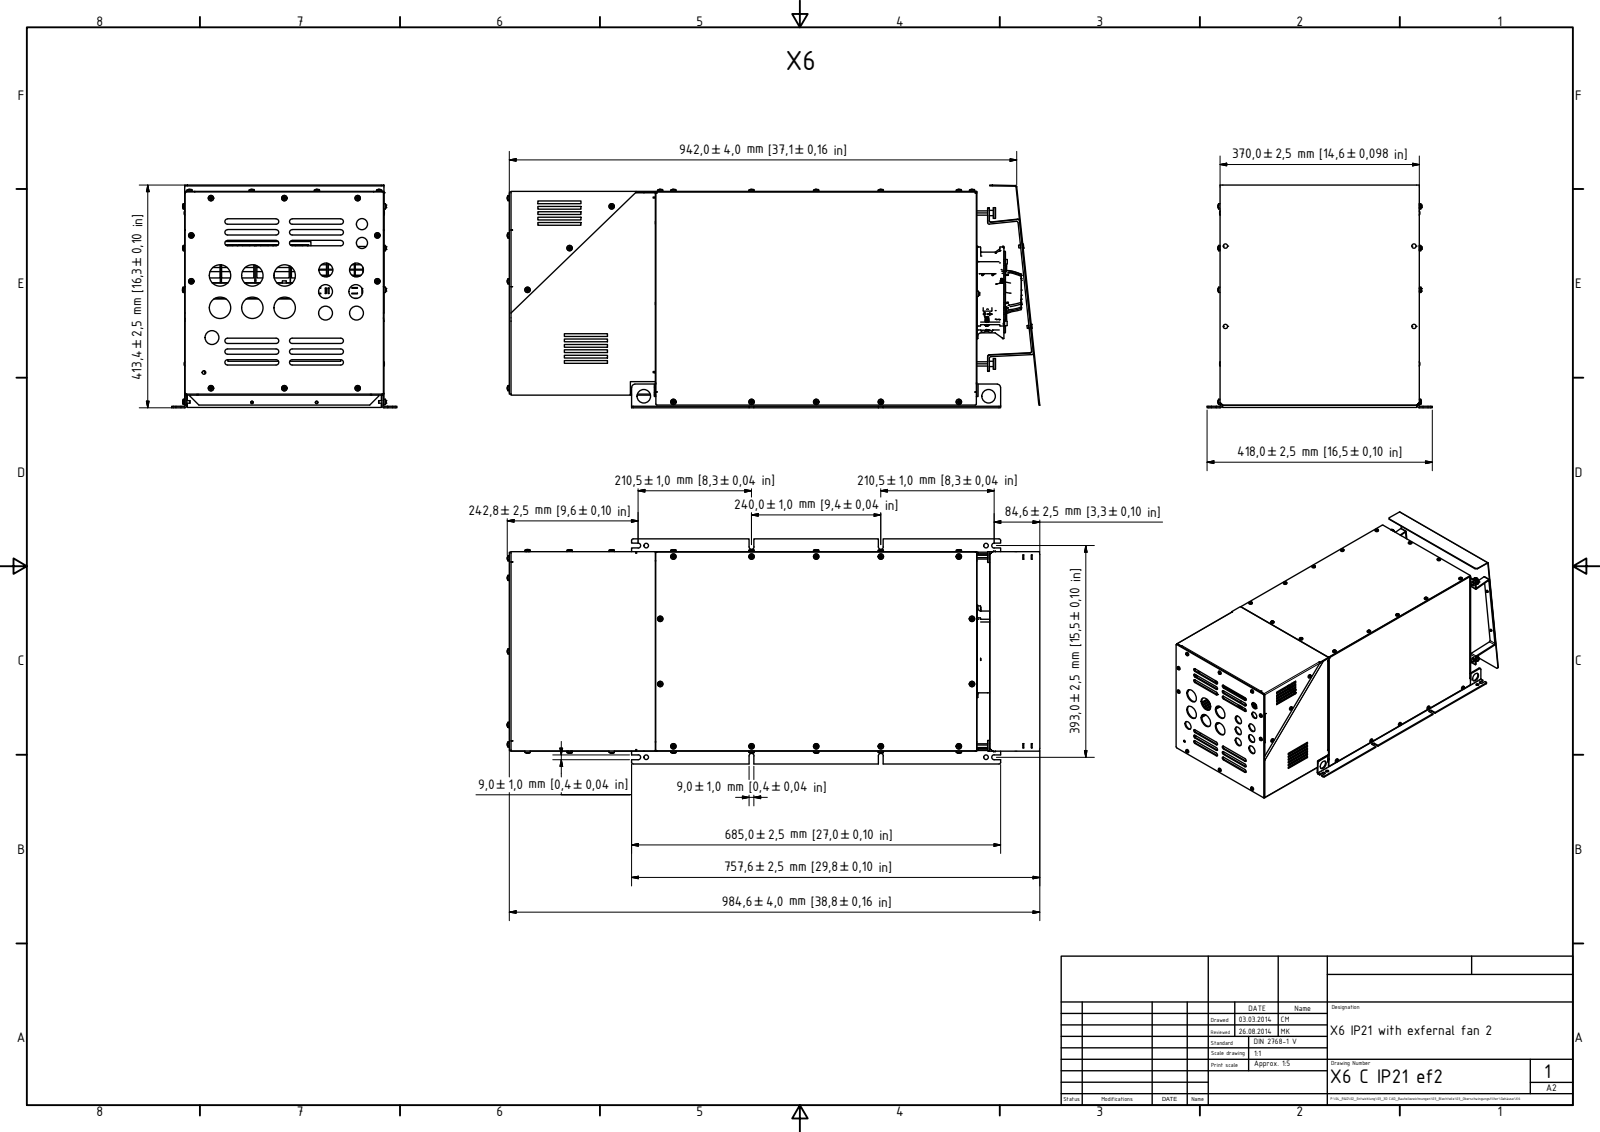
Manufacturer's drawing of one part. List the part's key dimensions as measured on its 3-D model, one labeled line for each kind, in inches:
Part name (STEP PRODUCT): 10100398 Deckel X5_X6; 10100402 Seitenwand X6; 10100400 Anschlussblech X6; 10100401 Lüfterblech X6 (+8 more)
STEP written by: Autodesk Inventor 2015 (AUTOMOTIVE_DESIGN)
Units: inches
Bodies: 160 solids, 13230 faces (7713 planar, 2703 cylindrical, 2814 other)
Overall size (bounding box): 38.914 × 16.457 × 16.277
Volume: 298.3 in³ · Surface area: 7 710 in²
Round holes (diameter × count): ⌀0.163 ×40, ⌀0.256 ×38, ⌀0.157 ×13, ⌀0.325 ×12, ⌀0.354 ×8, ⌀0.128 ×7, ⌀1.004 ×7, ⌀0.217 ×6, ⌀0.335 ×6, ⌀1.575 ×6, ⌀0.177 ×4, ⌀0.323 ×4
Round bosses / shafts (diameter × count): ⌀0.197 ×45, ⌀0.181 ×43, ⌀0.315 ×18, ⌀0.709 ×12, ⌀0.157 ×7, ⌀0.098 ×6, ⌀0.394 ×5, ⌀0.335 ×5
Partial cylindrical surfaces — rounded edges, fillets, slot ends (radius × count): R0.02 ×235, R0.009 ×112, R0.012 ×78, R0.039 ×67, R0.079 ×47, R0.197 ×47, R0.118 ×46, R0.004 ×37
Main face-to-face distances: 0.039, 0.079, 14.528, 14.488, 0.118, 14.567, 14.764, 14.843, 23.465, 14.882
Hole centre spacings: 13.858, 4.724, 5.906, 13.78, 5.709, 10.433, 15.157, 0.709
